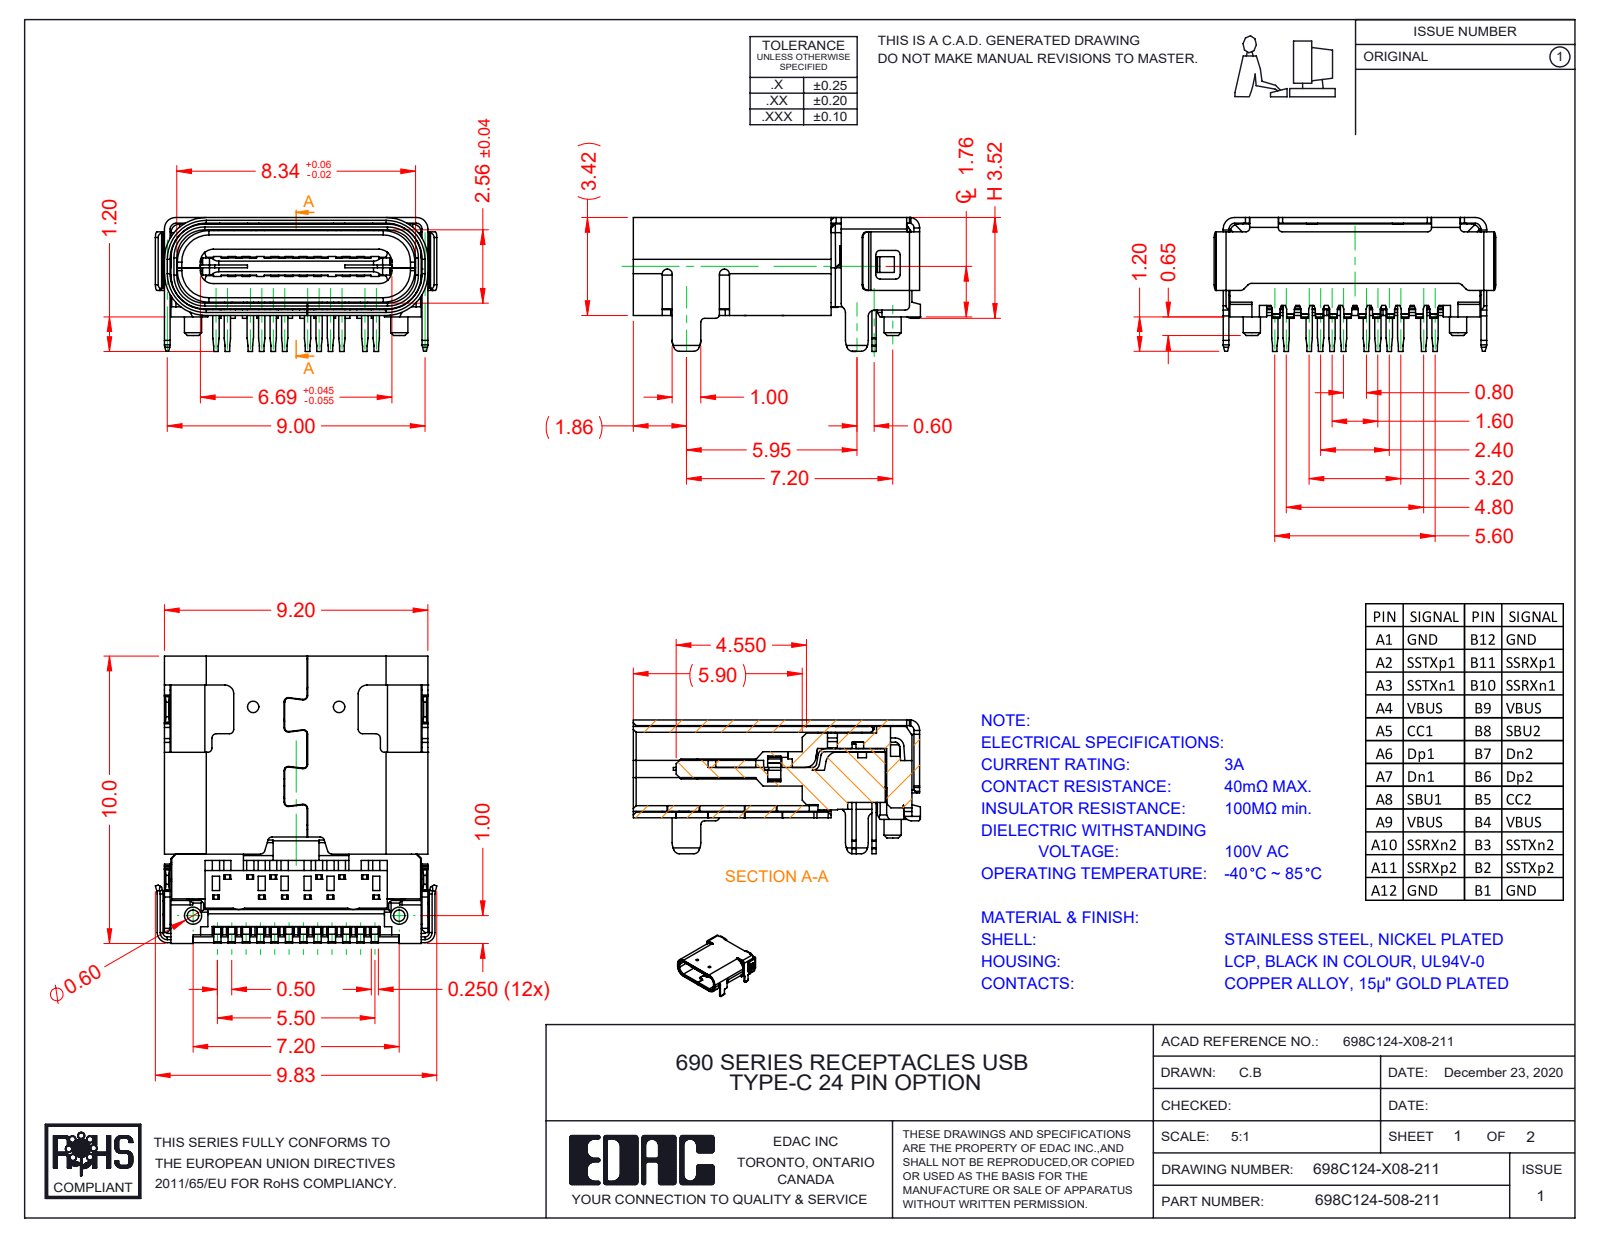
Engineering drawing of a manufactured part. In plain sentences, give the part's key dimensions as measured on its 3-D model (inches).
The part is named "Insulator2 698C124-X08-211; 698C124-208-211; Insulator1 698C124-X08-211; Shell 698C124-X08-211". Its 3-D file was written by "SolidWorks 2020 (AUTOMOTIVE_DESIGN)". It is 3 solids with 3138 faces: 2372 planar, 671 cylindrical and 95 other. Overall it measures 0.395 by 0.387 by 0.184 inches. Its volume is 0.01 cubic inches and its surface area 2.206 square inches. Round holes: 2 of diameter 0.016, 2 of diameter 0.02, 2 of diameter 0.024, 2 of diameter 0.026. Round bosses or shafts: 4 of diameter 0.024. Partial cylindrical surfaces (rounded edges, fillets, slot ends): 100 of radius 0.006, 58 of radius 0.012, 36 of radius 0.004, 31 of radius 0.008, 30 of radius 0.005, 10 of radius 0.014, 5 of radius 0.007, 5 of radius 0.01. The main face-to-face distances are 0.118, 0.017, 0.11, 0.109, 0.126, 0.127, 0.035, 0.022, 0.016, 0.101. The hole center spacings are 0.081, 0.135, 0.145, 0.178, 0.226, 0.253, 0.098, 0.1.
